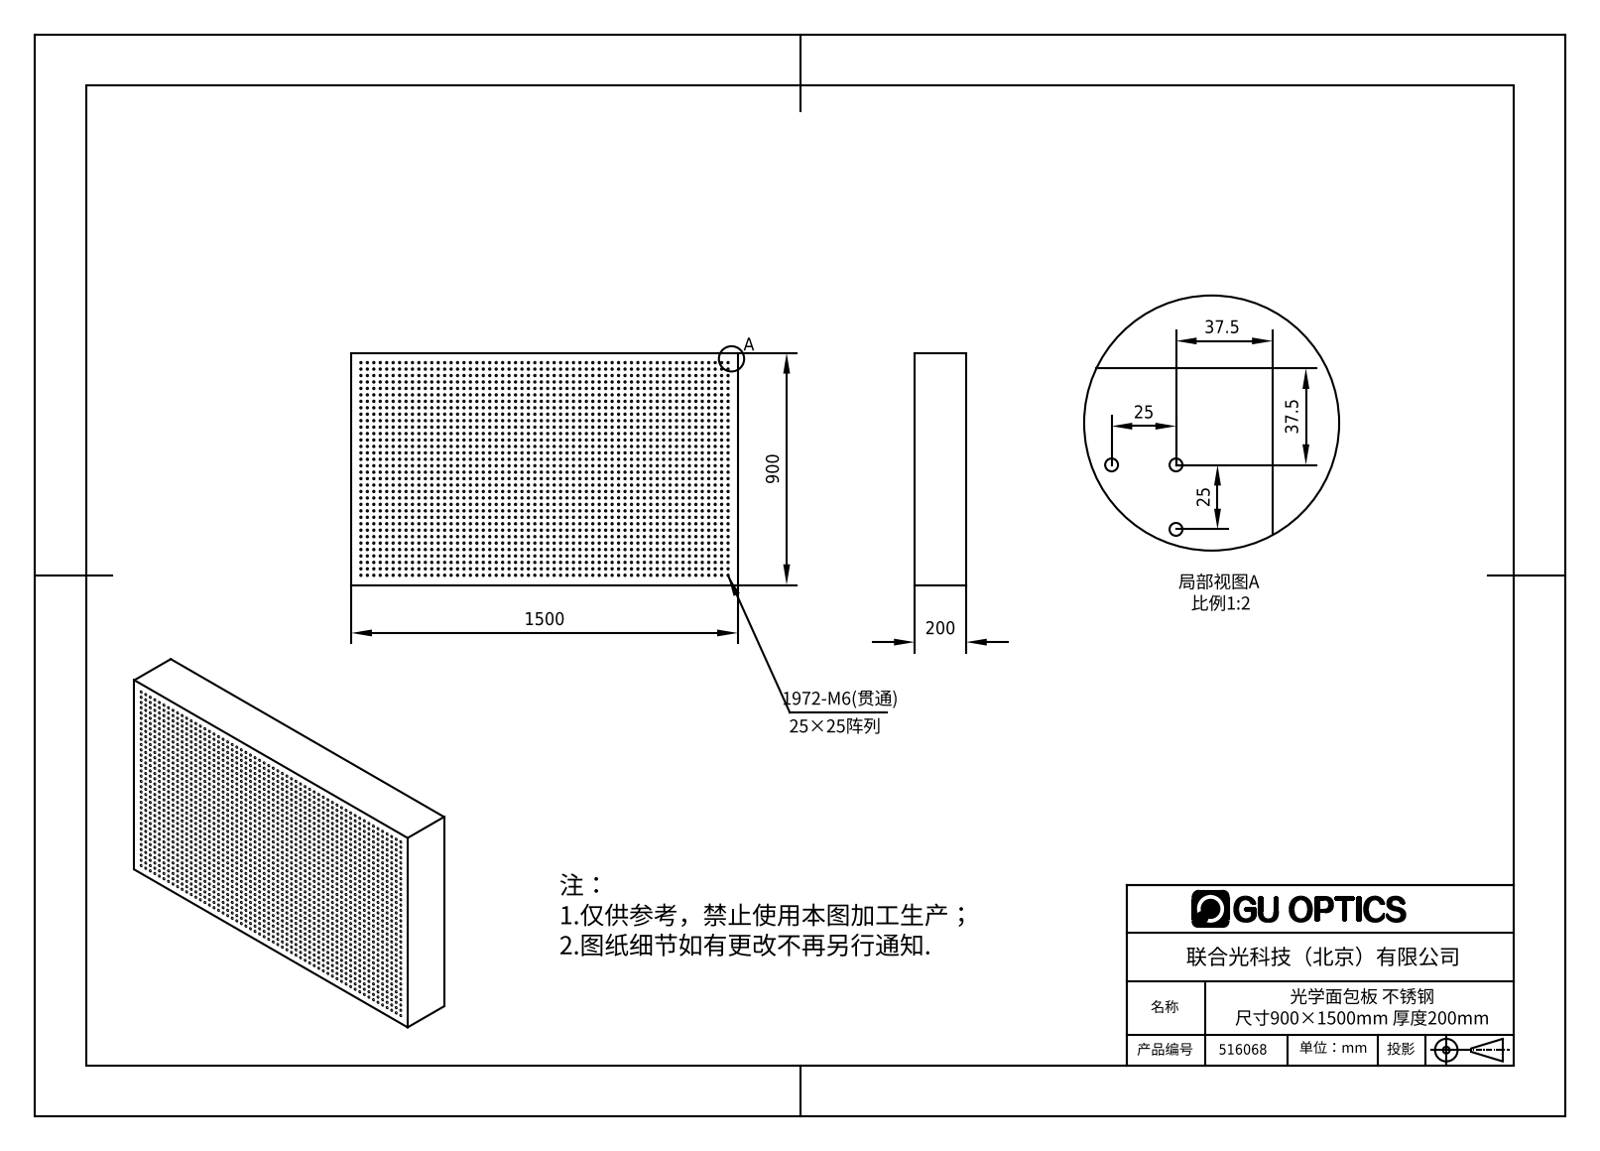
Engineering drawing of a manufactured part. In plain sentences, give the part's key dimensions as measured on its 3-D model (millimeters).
The part is named "516068". Its 3-D file was written by "SolidWorks 2016 (AUTOMOTIVE_DESIGN)". It is 1 solid with 3950 faces: 6 planar, 3944 cylindrical and 0 other. Overall it measures 1500 by 900 by 200 millimeters. Its volume is 262 300 000 cubic millimeters and its surface area 9 778 000 square millimeters. Round holes: 1972 of diameter 5. The main face-to-face distances are 200, 900, 1500. The hole center spacings are 25, 50, 75, 100, 125, 150, 175, 200.
